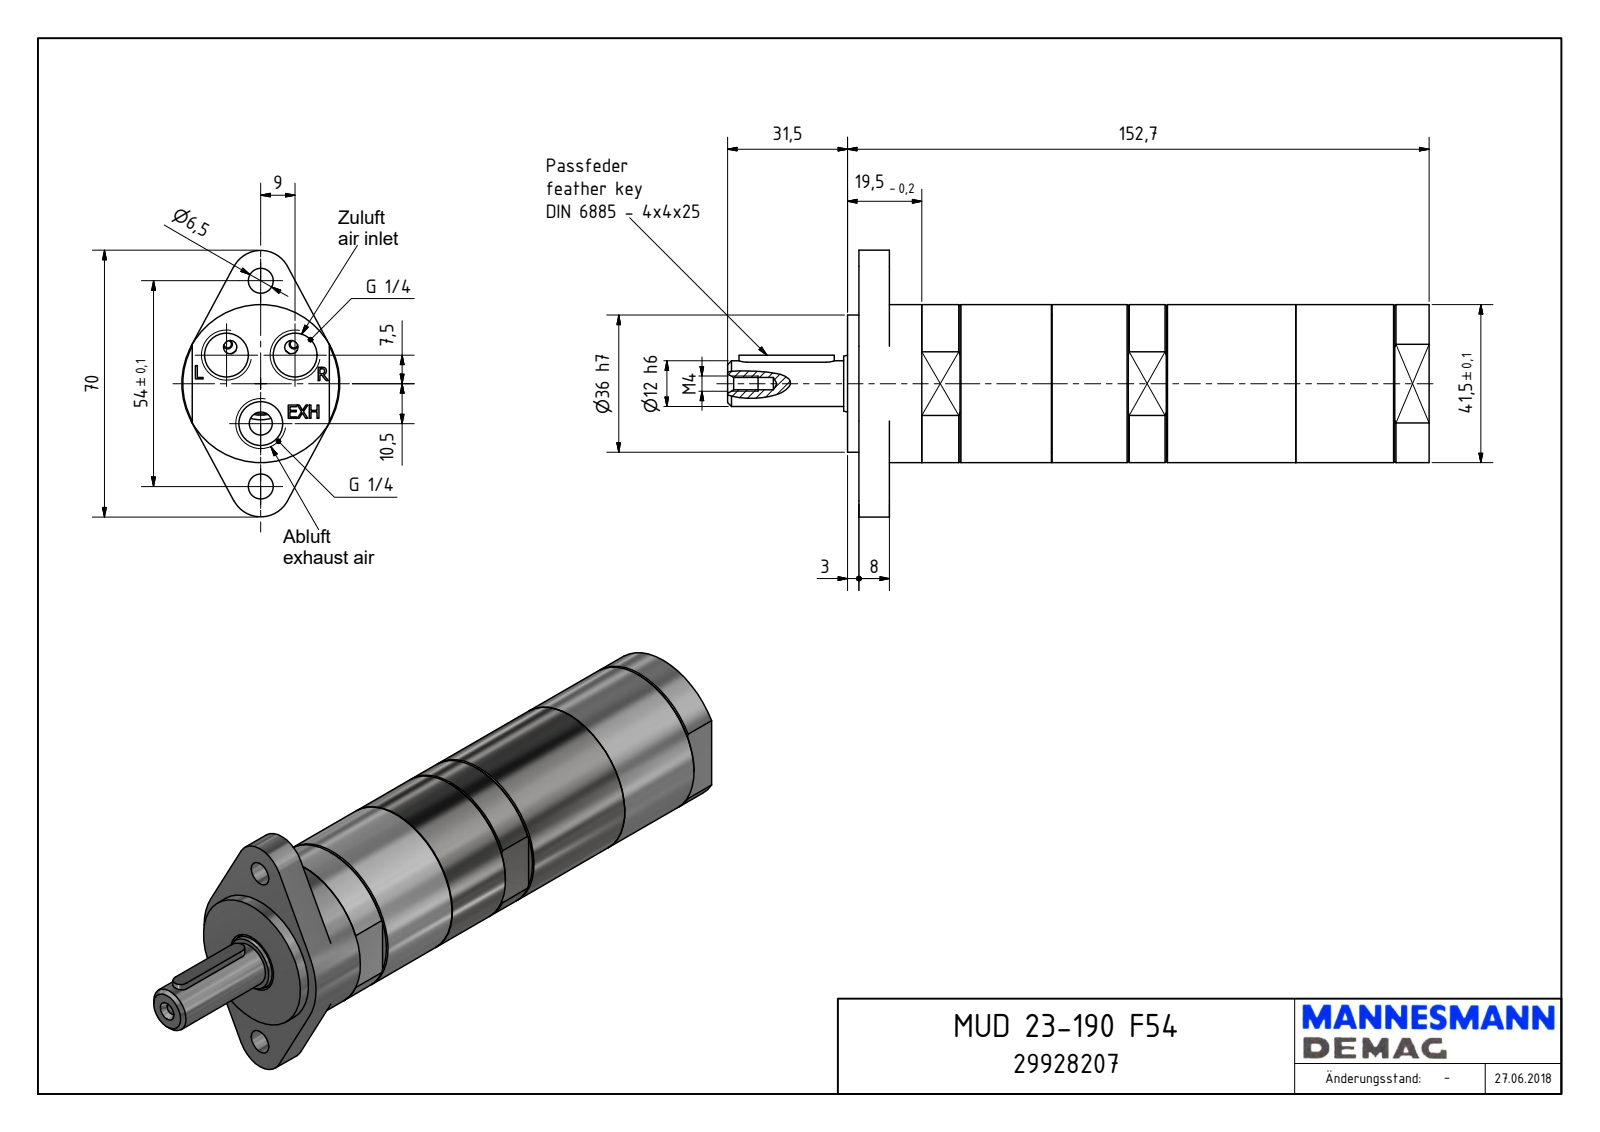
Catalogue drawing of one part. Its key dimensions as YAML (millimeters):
part_name: "MUD 23-190 F54_29928207"
step_written_by: "Autodesk Inventor 2018 (AUTOMOTIVE_DESIGN)"
units: millimeters
bodies: {solids: 1, faces: 153, planar: 98, cylindrical: 27, other: 28}
overall_size: [184.2, 70, 41.5]
volume: 208485
surface_area: 27837
round_holes:
  - {diameter: 11.45, count: 3}
  - {diameter: 6.5, count: 2}
  - {diameter: 3.24, count: 1}
  - {diameter: 16, count: 1}
  - {diameter: 23, count: 1}
round_bosses_or_shafts:
  - {diameter: 41.5, count: 1}
  - {diameter: 36, count: 1}
  - {diameter: 14.95, count: 1}
  - {diameter: 12, count: 1}
partial_cylinders:
  - {radius: 2, count: 2}
  - {radius: 8, count: 2}
face_to_face_distances: [3, 149.7, 152.7, 141.7, 11, 8, 1, 42.5, 41.48, 37]
hole_center_spacings: [11.72, 20.12, 21.48, 27, 35.65, 10.5, 16.5, 18]
